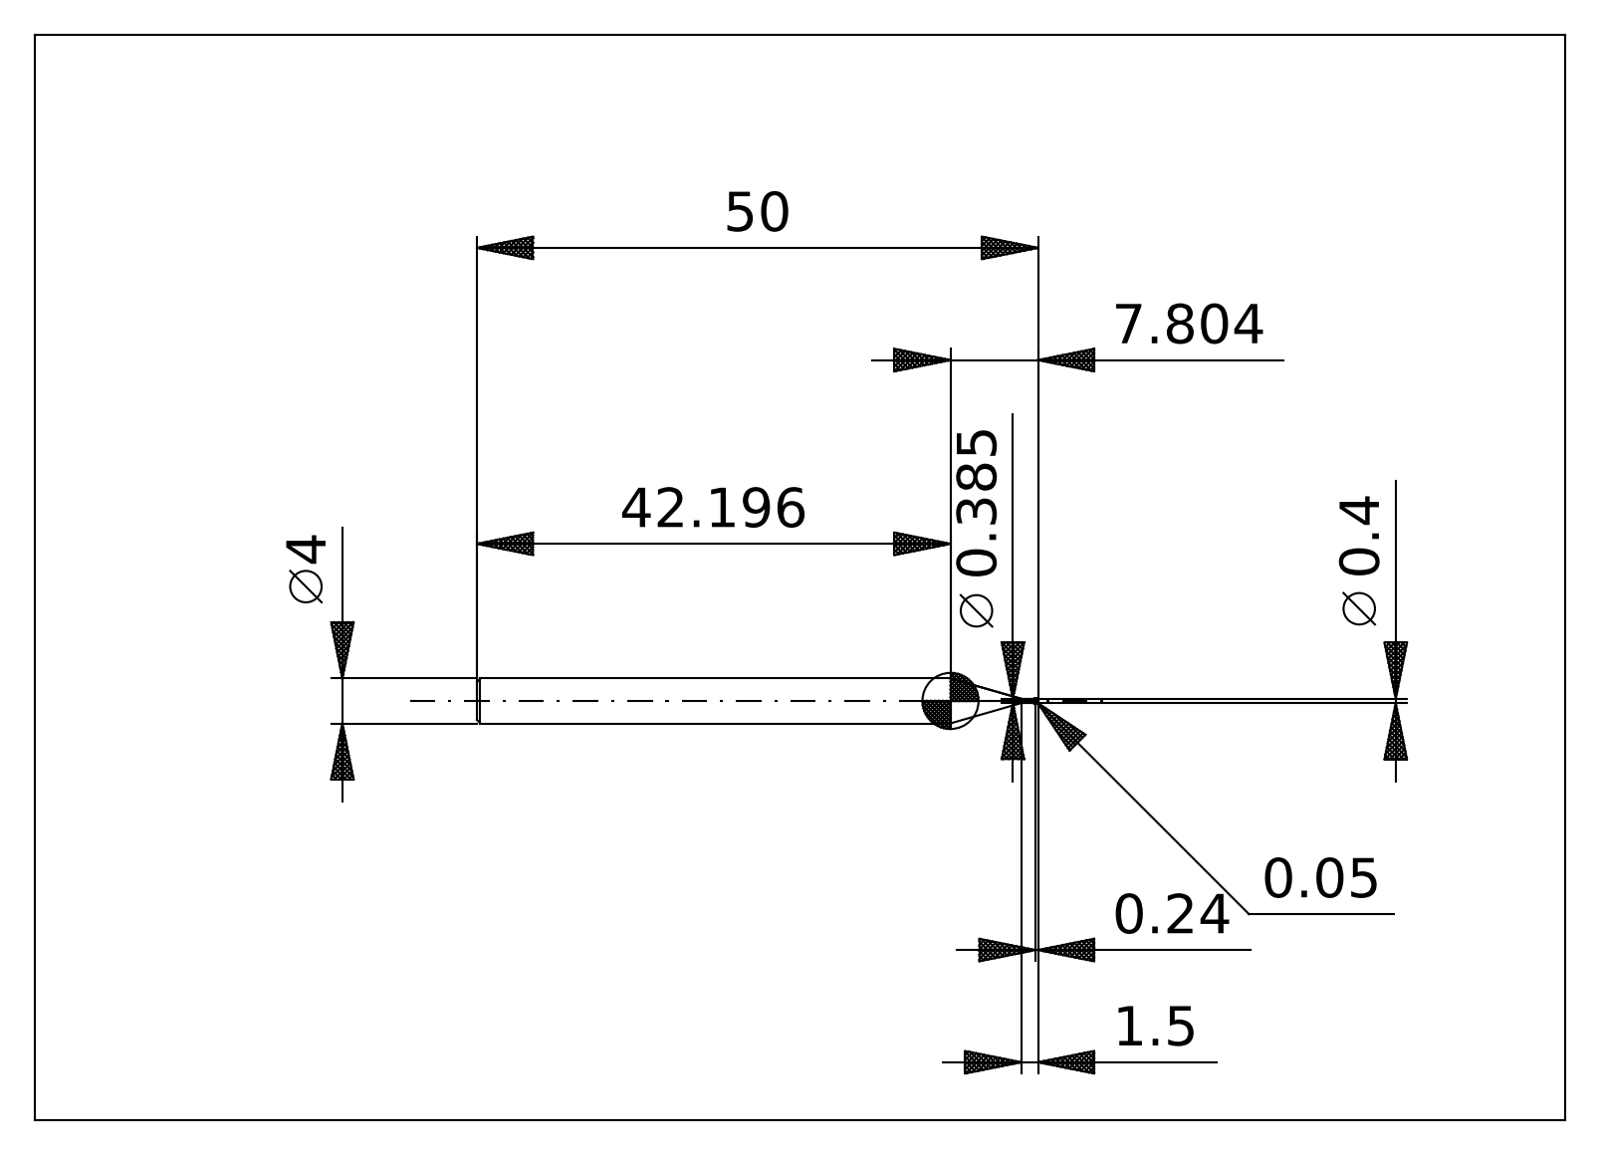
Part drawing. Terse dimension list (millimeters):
written by: ACIS (automotive_design)
unit: mm
bodies: 2 solids, 26 faces (6 planar, 8 cylindrical, 12 other)
size: 50 × 4 × 4
volume: 559 mm³; area: 588 mm²
bosses: 1× ⌀4, 1× ⌀0.38
face distances: 50, 49.94, 49.76, 7.8, 7.74, 7.56, 42.2
